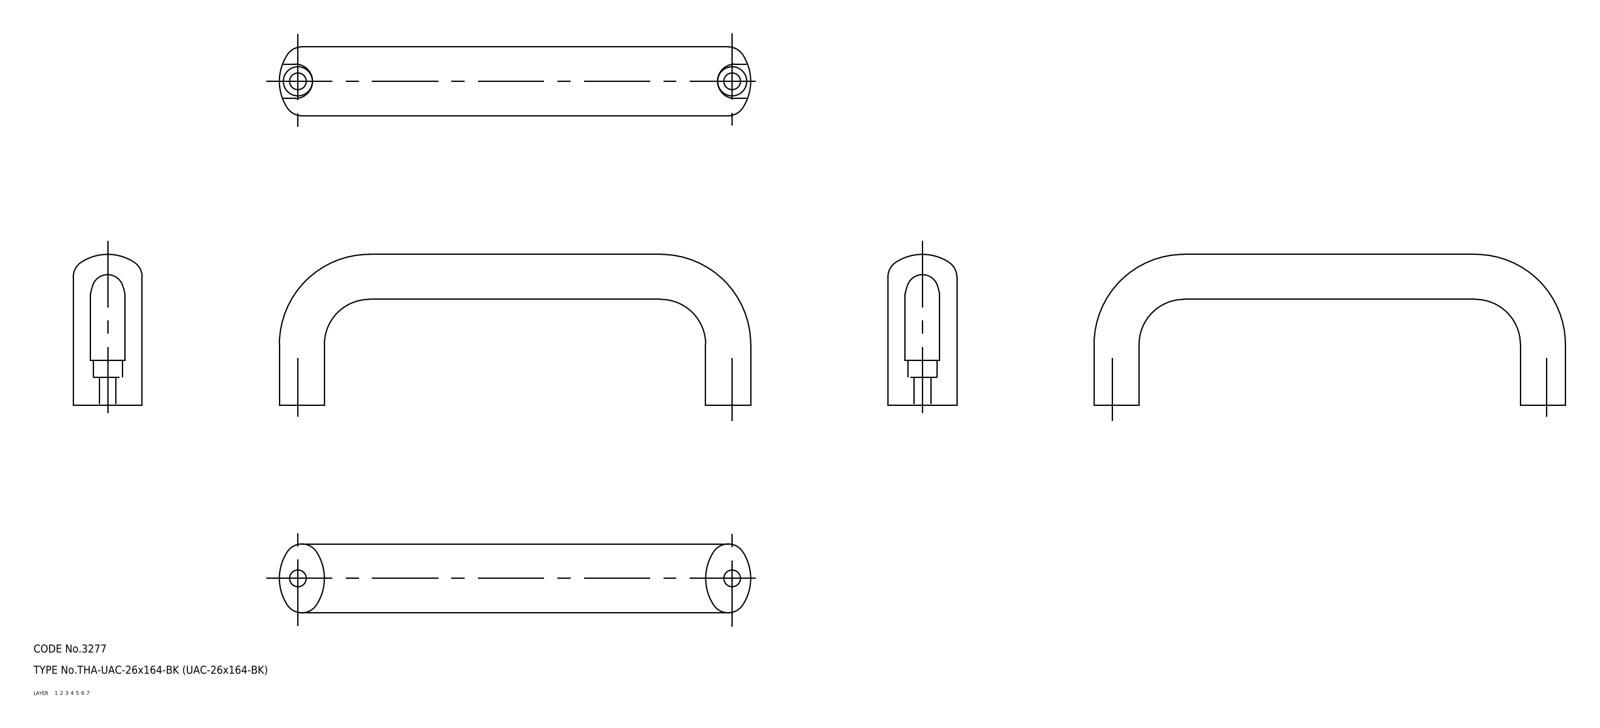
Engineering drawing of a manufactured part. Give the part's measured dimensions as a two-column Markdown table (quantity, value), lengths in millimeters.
| quantity | value |
| --- | --- |
| part name | pull |
| STEP written by | CADfix (AUTOMOTIVE_DESIGN) |
| units | millimeters |
| bodies | 1 solid, 30 faces (0 planar, 0 cylindrical, 30 other) |
| overall size | 178 × 57 × 26 |
| volume | 73 562 mm³ |
| surface area | 18 479 mm² |
